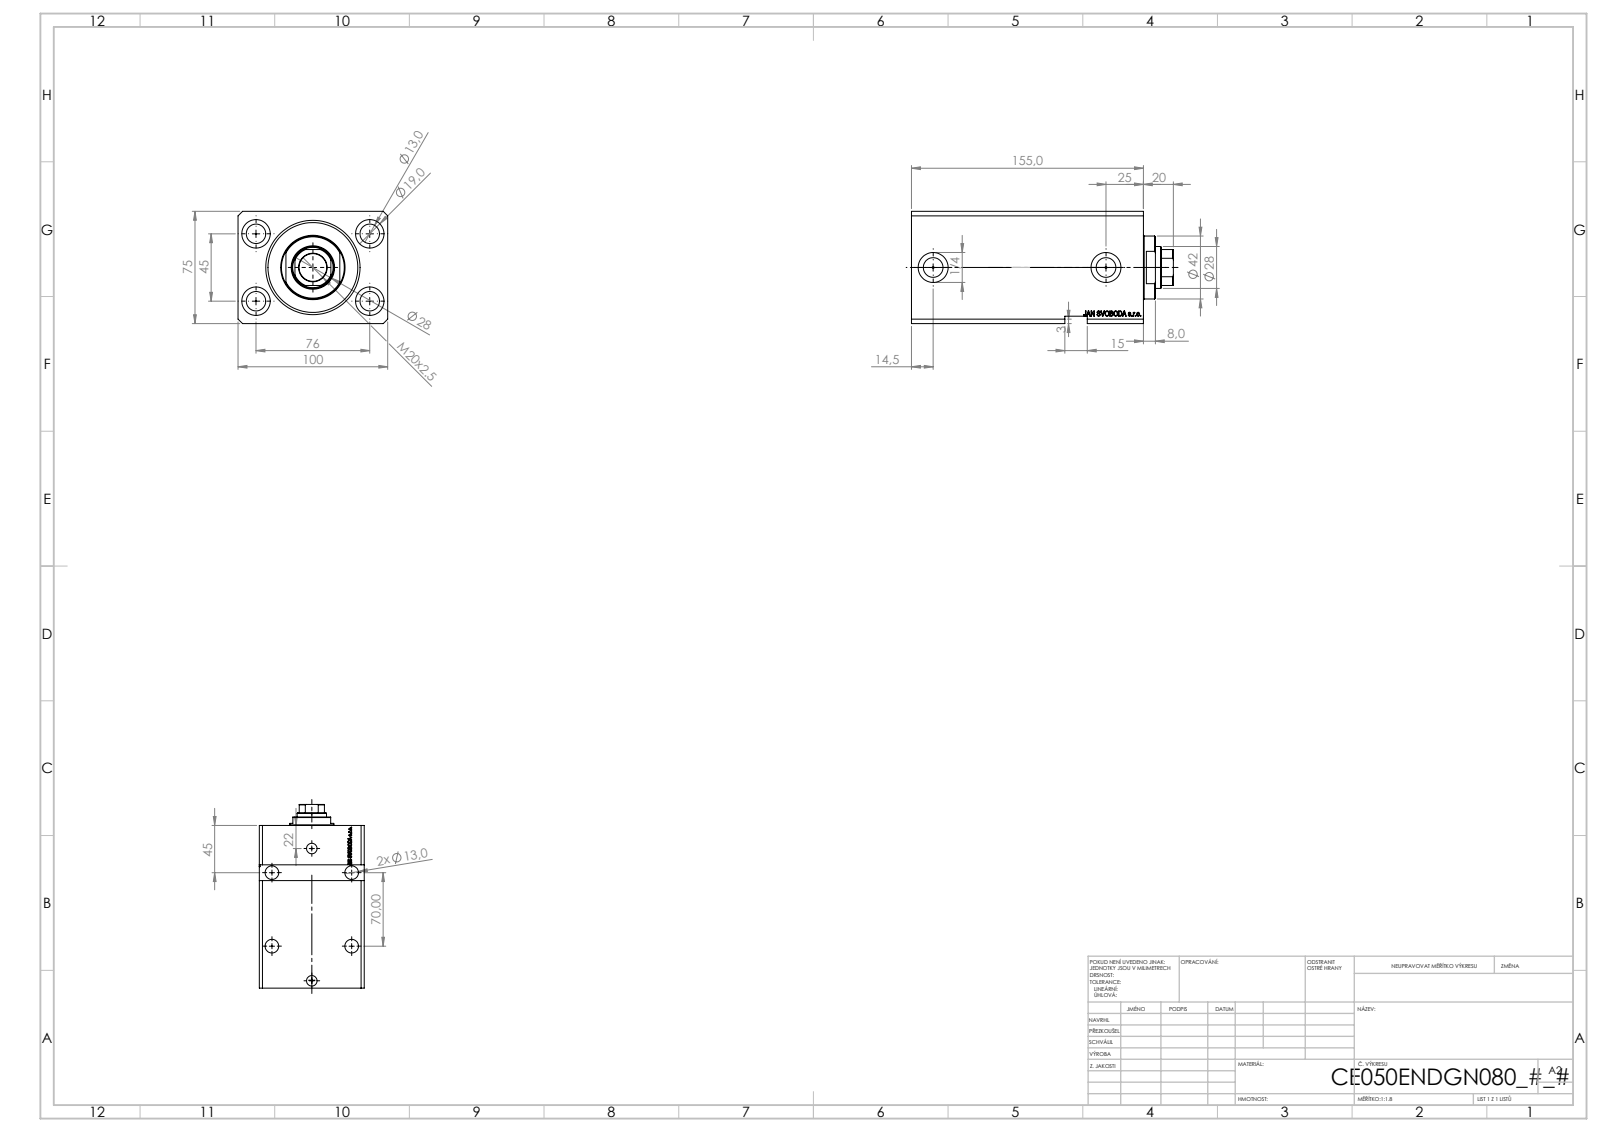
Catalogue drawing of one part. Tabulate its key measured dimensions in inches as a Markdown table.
| quantity | value |
| --- | --- |
| part name | V250CE_C_VCP; V250CE_E_Body; V250CE_VC_E |
| STEP written by | SolidWorks 2019 (CONFIG_CONTROL_DESIGN) |
| units | inches |
| bodies | 3 solids, 954 faces (463 planar, 116 cylindrical, 375 other) |
| overall size | 6.89 × 3.937 × 2.953 |
| volume | 56.09 in³ |
| surface area | 251.6 in² |
| round holes (diameter × count) | 0.512 × 8, 0.049 × 4, 0.748 × 4, 0.394 × 2, 0.518 × 2, 0.787 × 2, 0.728 × 1, 1.102 × 1, 1.969 × 1, 2.48 × 1 |
| round bosses / shafts (diameter × count) | 1.654 × 1 |
| partial cylindrical surfaces (radius × count) | 0.531 × 1 |
| main face-to-face distances | 2.953, 3.937, 6.102, 0.469, 5.634, 0.787, 5.315, 4.846, 0.512, 2.165 |
| hole center spacings | 1.739, 2.992, 1.749, 1.772, 1.968, 1.981, 2.756, 3.477 |
